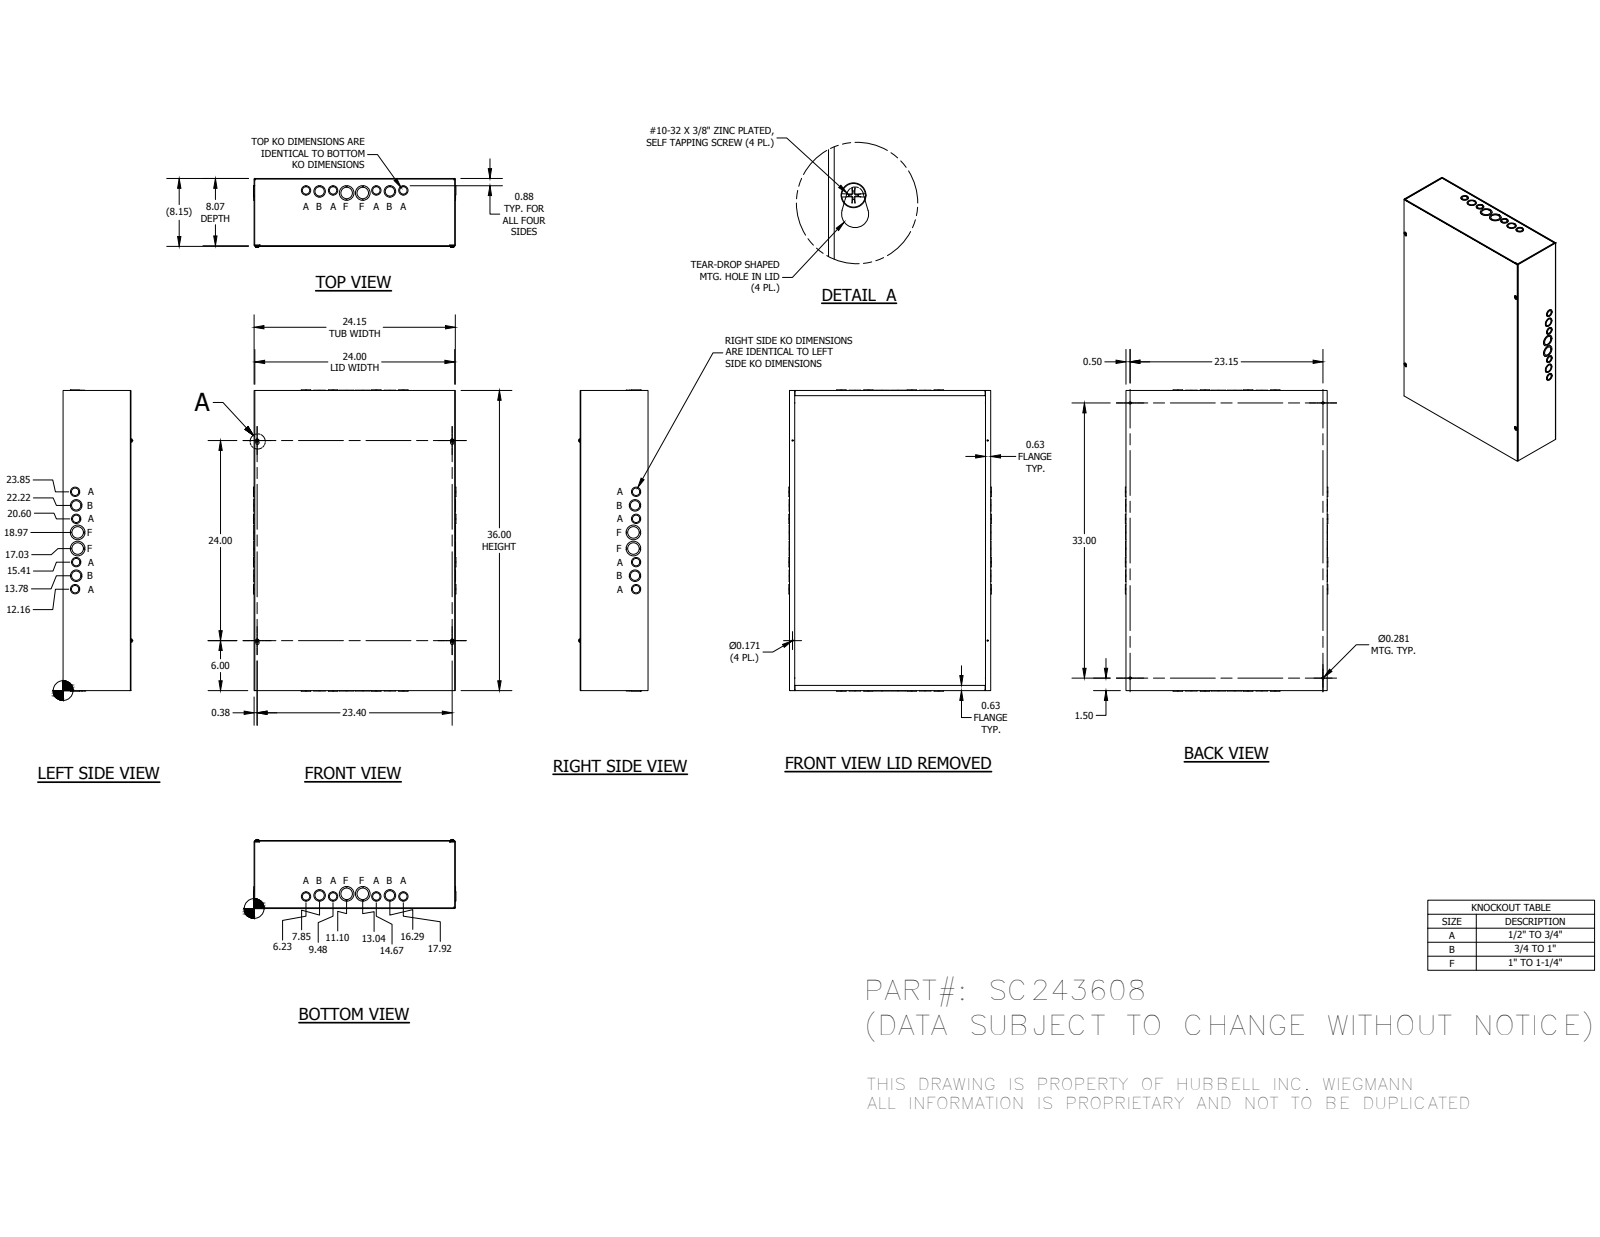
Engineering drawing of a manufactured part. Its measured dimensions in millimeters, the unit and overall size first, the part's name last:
Units: millimetres
Overall size (bounding box): 918.16 × 617.12 × 210.31
Round holes (diameter × count): ⌀28.57 ×14, ⌀22.22 ×10, ⌀34.92 ×8, ⌀4.34 ×4, ⌀7.14 ×4, ⌀44.45 ×4
Round bosses / shafts (diameter × count): ⌀4.83 ×4
Partial cylindrical surfaces — rounded edges, fillets, slot ends (radius × count): R0.4 ×12, R2.28 ×12, R3.17 ×4, R5.16 ×4
Main face-to-face distances: 1.88, 205.08, 203.2, 206.96, 611.48, 912.52, 609.6, 613.36, 914.4, 910.64
Hole centre spacings: 41.39, 41.4, 42.03, 82.55, 82.69, 90.9, 114.34, 124.07
Bodies: 37 solids, 1219 faces (899 planar, 236 cylindrical, 84 other)
Part name (STEP PRODUCT): SC243608BLR; SC2408TB; SC2436LPA; 37214 (+1 more)
STEP written by: Autodesk Inventor 2014 (AUTOMOTIVE_DESIGN)
